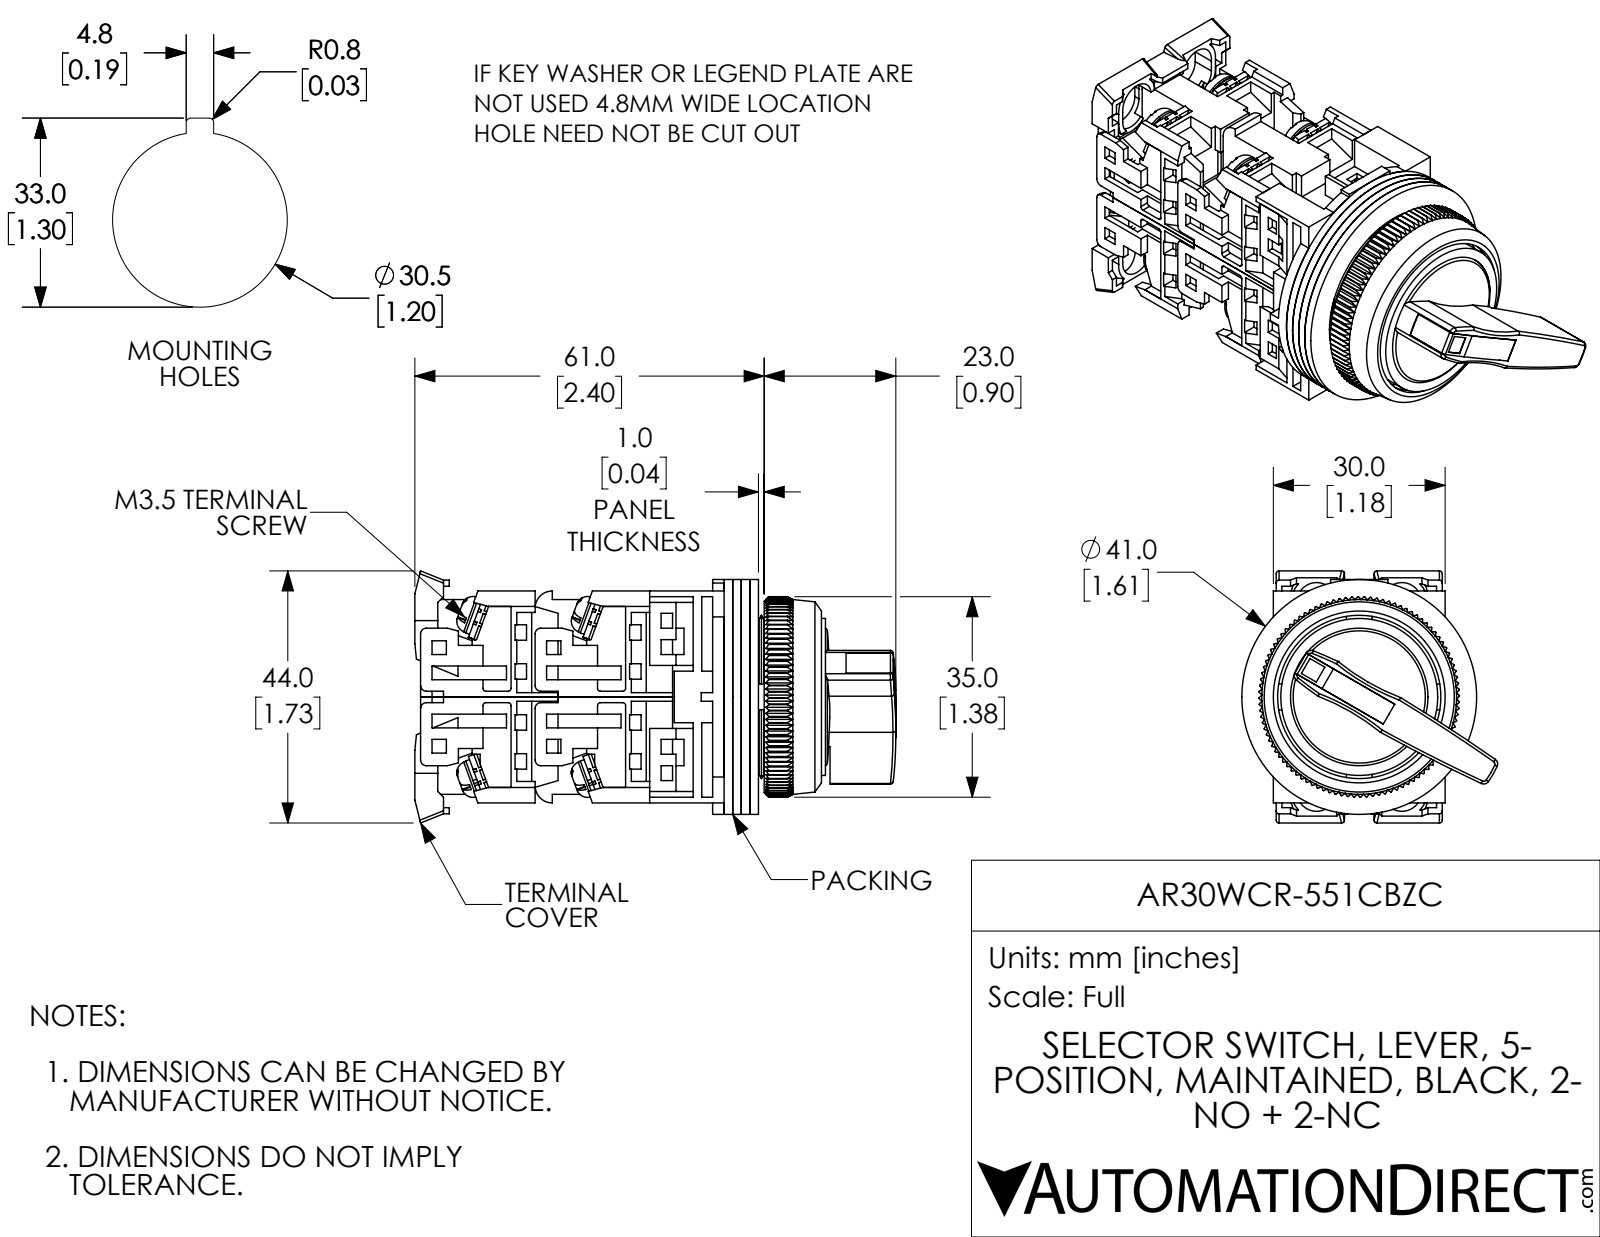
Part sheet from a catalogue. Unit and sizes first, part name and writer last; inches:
Units: inches
Overall size (bounding box): 3.307 × 1.759 × 1.732
Round holes (diameter × count): ⌀0.138 ×14, ⌀0.142 ×8, ⌀0.118 ×1, ⌀0.315 ×1, ⌀0.472 ×1, ⌀0.48 ×1, ⌀0.512 ×1, ⌀0.819 ×1, ⌀0.945 ×1, ⌀1.122 ×1, ⌀1.181 ×1, ⌀1.252 ×1
Round bosses / shafts (diameter × count): ⌀0.26 ×8, ⌀0.138 ×8, ⌀1.614 ×1, ⌀1.15 ×1, ⌀1.079 ×1, ⌀0.787 ×1, ⌀0.709 ×1, ⌀0.669 ×1
Partial cylindrical surfaces — rounded edges, fillets, slot ends (radius × count): R0.059 ×32, R0.02 ×17, R0.039 ×12, R0.118 ×4, R0.138 ×4, R0.177 ×4, R1.575 ×2, R1.638 ×2
Main face-to-face distances: 0.059, 0.118, 0.039, 0.787, 0.063, 0.177, 0.079, 0.02, 0.689, 0.028
Hole centre spacings: 0.579, 0.269, 0.638, 0.61
Volume: 3.212 in³ · Surface area: 77.35 in²
Bodies: 40 solids, 2519 faces (1908 planar, 353 cylindrical, 258 other)
Part name (STEP PRODUCT): AR30WCR-551CBZC
STEP written by: SolidWorks 2017 (AUTOMOTIVE_DESIGN)
